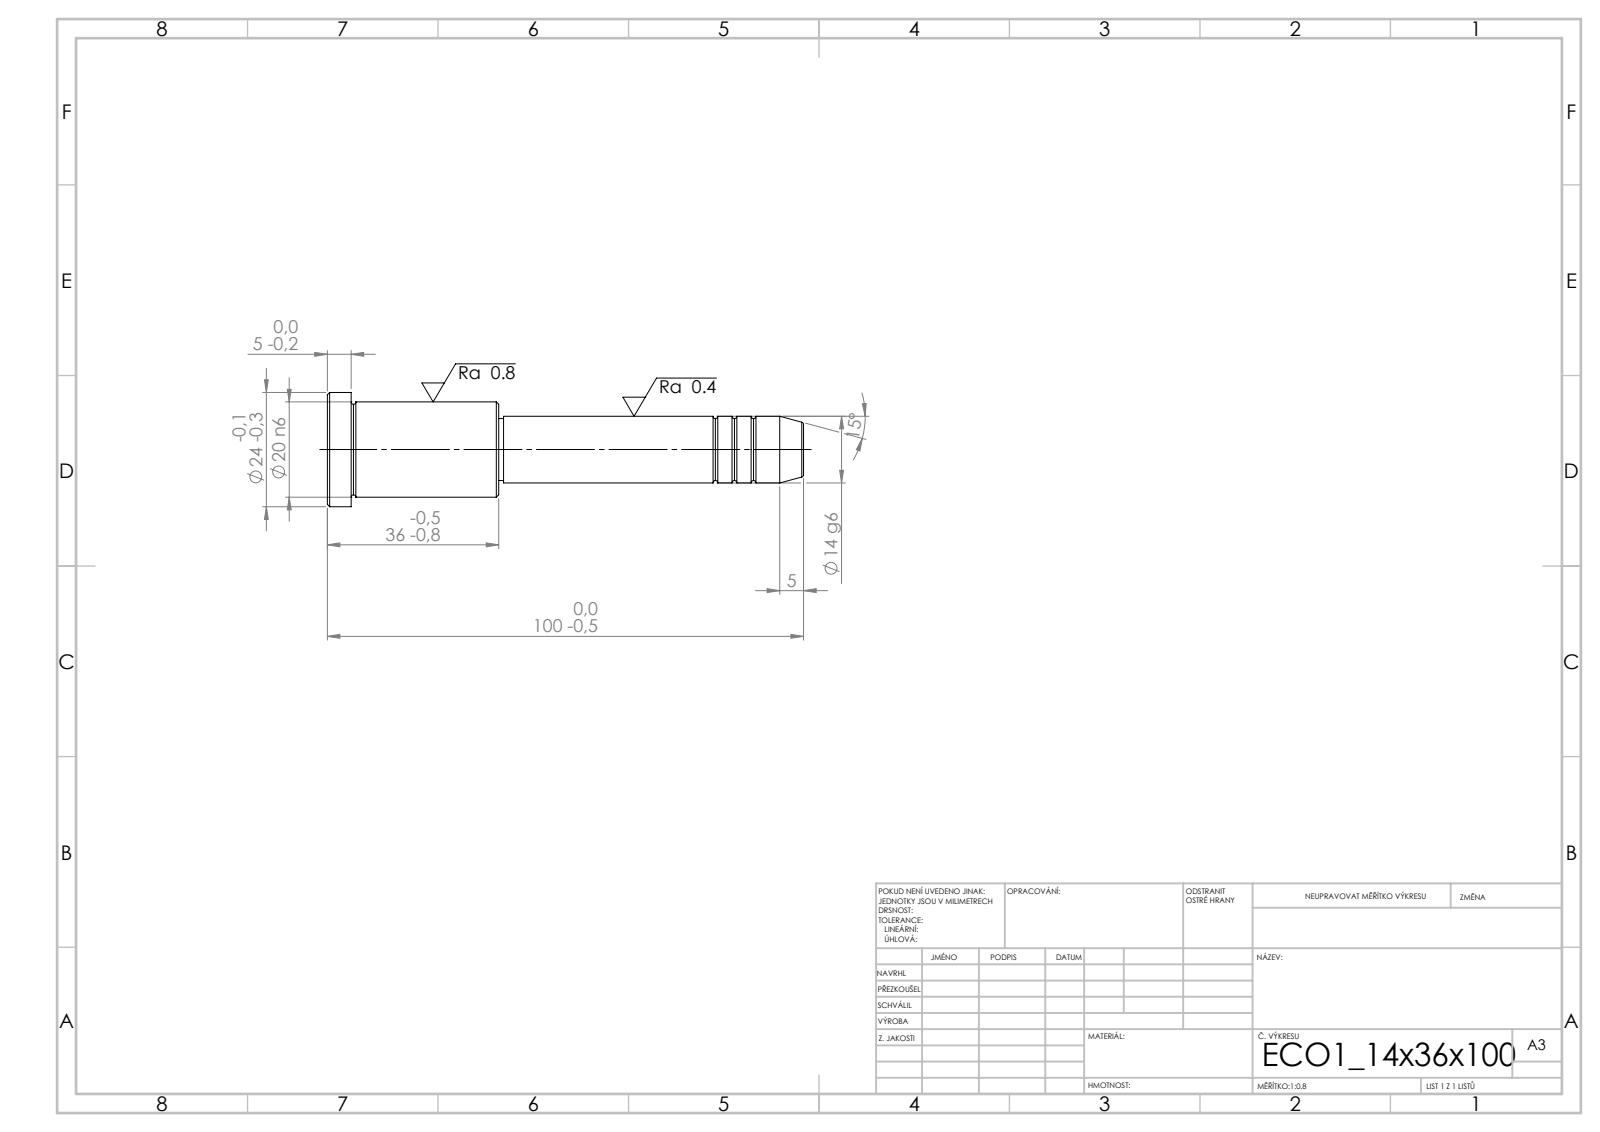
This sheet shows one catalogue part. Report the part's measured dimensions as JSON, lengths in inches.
{"step_written_by": "SolidWorks 2019 (CONFIG_CONTROL_DESIGN)", "units": "inches", "bodies": {"solids": 1, "faces": 43, "planar": 5, "cylindrical": 14, "other": 24}, "overall_size": [3.937, 0.945, 0.945], "volume_in3": 1.318, "surface_area_in2": 9.409, "round_bosses_or_shafts": [[0.945, 1], [0.787, 1], [0.551, 1], [0.512, 1]], "face_to_face_distances": [1.417, 1.22, 0.197, 2.52, 3.74, 3.937, 2.48, 0.039, 1.26, 1.457]}
